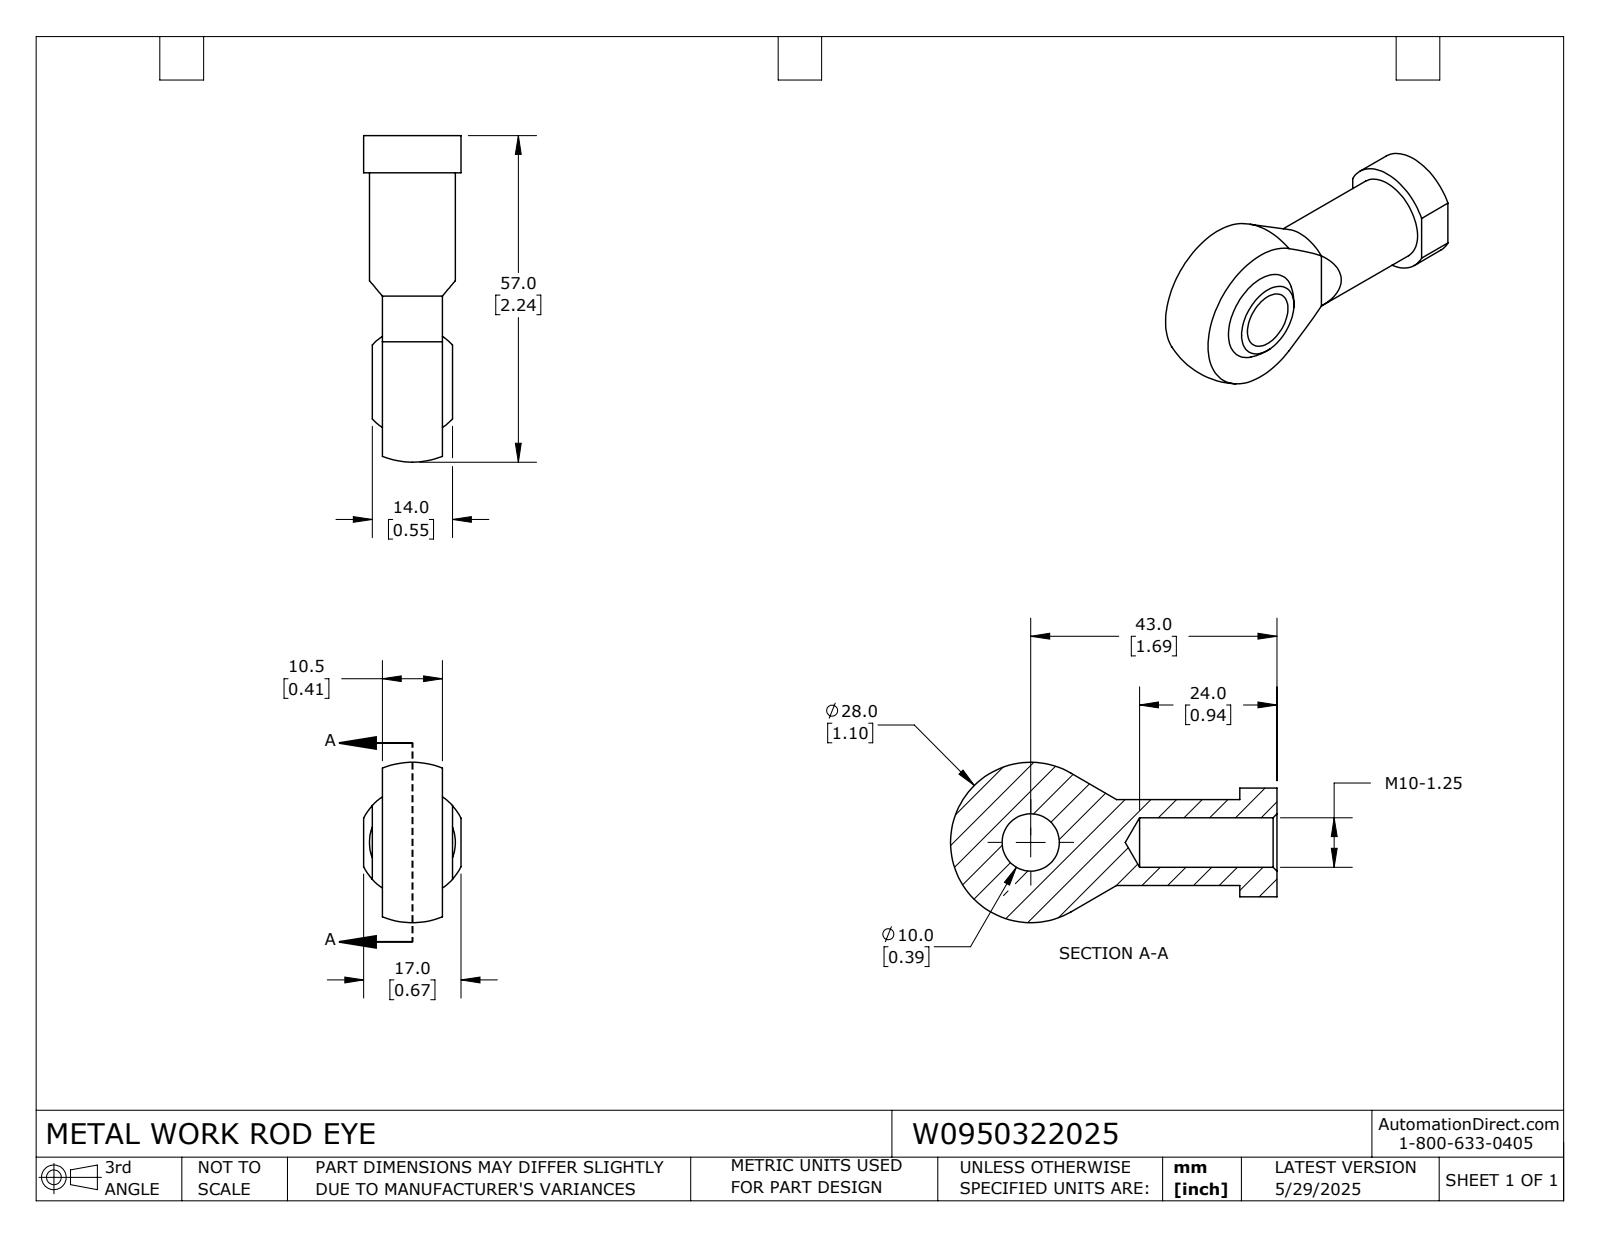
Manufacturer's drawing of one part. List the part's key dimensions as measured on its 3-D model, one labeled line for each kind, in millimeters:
Part name (STEP PRODUCT): W0950322025
STEP written by: SolidWorks 2024 (CONFIG_CONTROL_DESIGN)
Units: millimetres
Bodies: 1 solid, 28 faces (10 planar, 8 cylindrical, 10 other)
Overall size (bounding box): 57 × 28 × 17
Volume: 10 112 mm³ · Surface area: 4 746 mm²
Round holes (diameter × count): ⌀8.65 ×1, ⌀10 ×1
Round bosses / shafts (diameter × count): ⌀15 ×1
Partial cylindrical surfaces — rounded edges, fillets, slot ends (radius × count): R9.5 ×1
Main face-to-face distances: 10.5, 3.25, 13.75, 1.5, 15.5, 1.75, 12.25, 6.5, 17, 14
